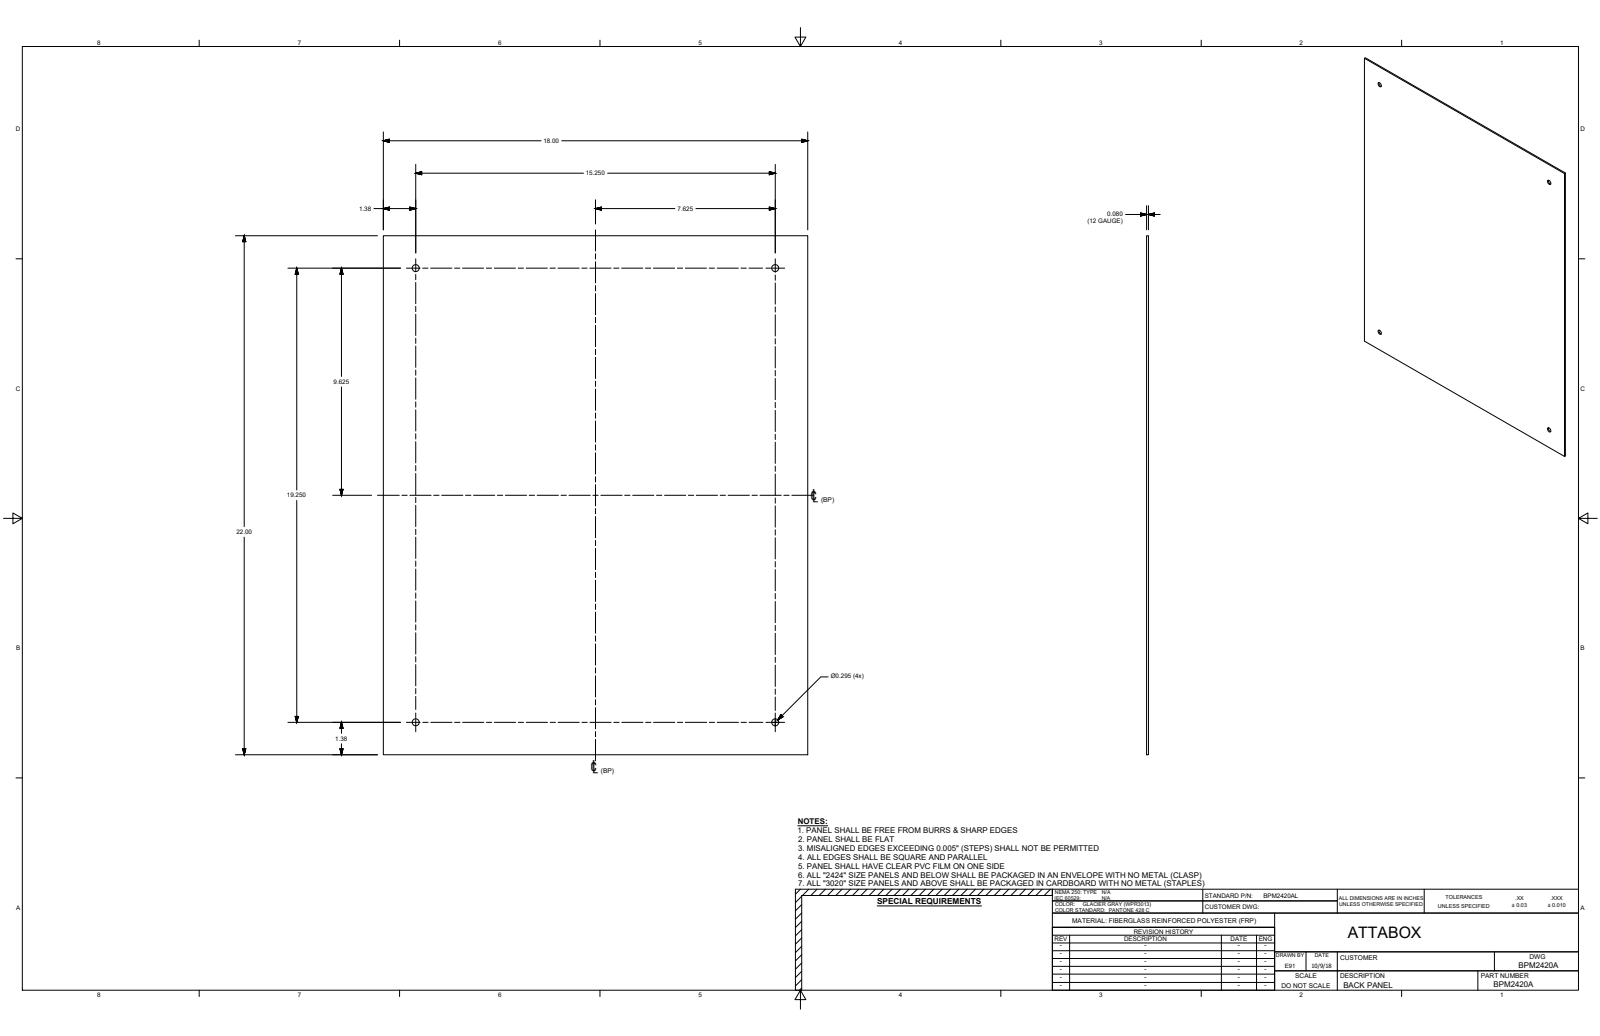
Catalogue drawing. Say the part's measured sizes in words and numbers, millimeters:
The part is named "HW-MP-2420AL". Its 3-D file was written by "Autodesk Inventor 2017 (CONFIG_CONTROL_DESIGN)". It is 1 solid with 10 faces: 6 planar, 4 cylindrical and 0 other. Overall it measures 558.8 by 457.2 by 2.03 millimeters. Its volume is 518 784 cubic millimeters and its surface area 514 934 square millimeters. Round holes: 4 of diameter 7.49. The main face-to-face distances are 2.03, 457.2, 558.8. The hole center spacings are 387.35, 488.96, 623.8.
